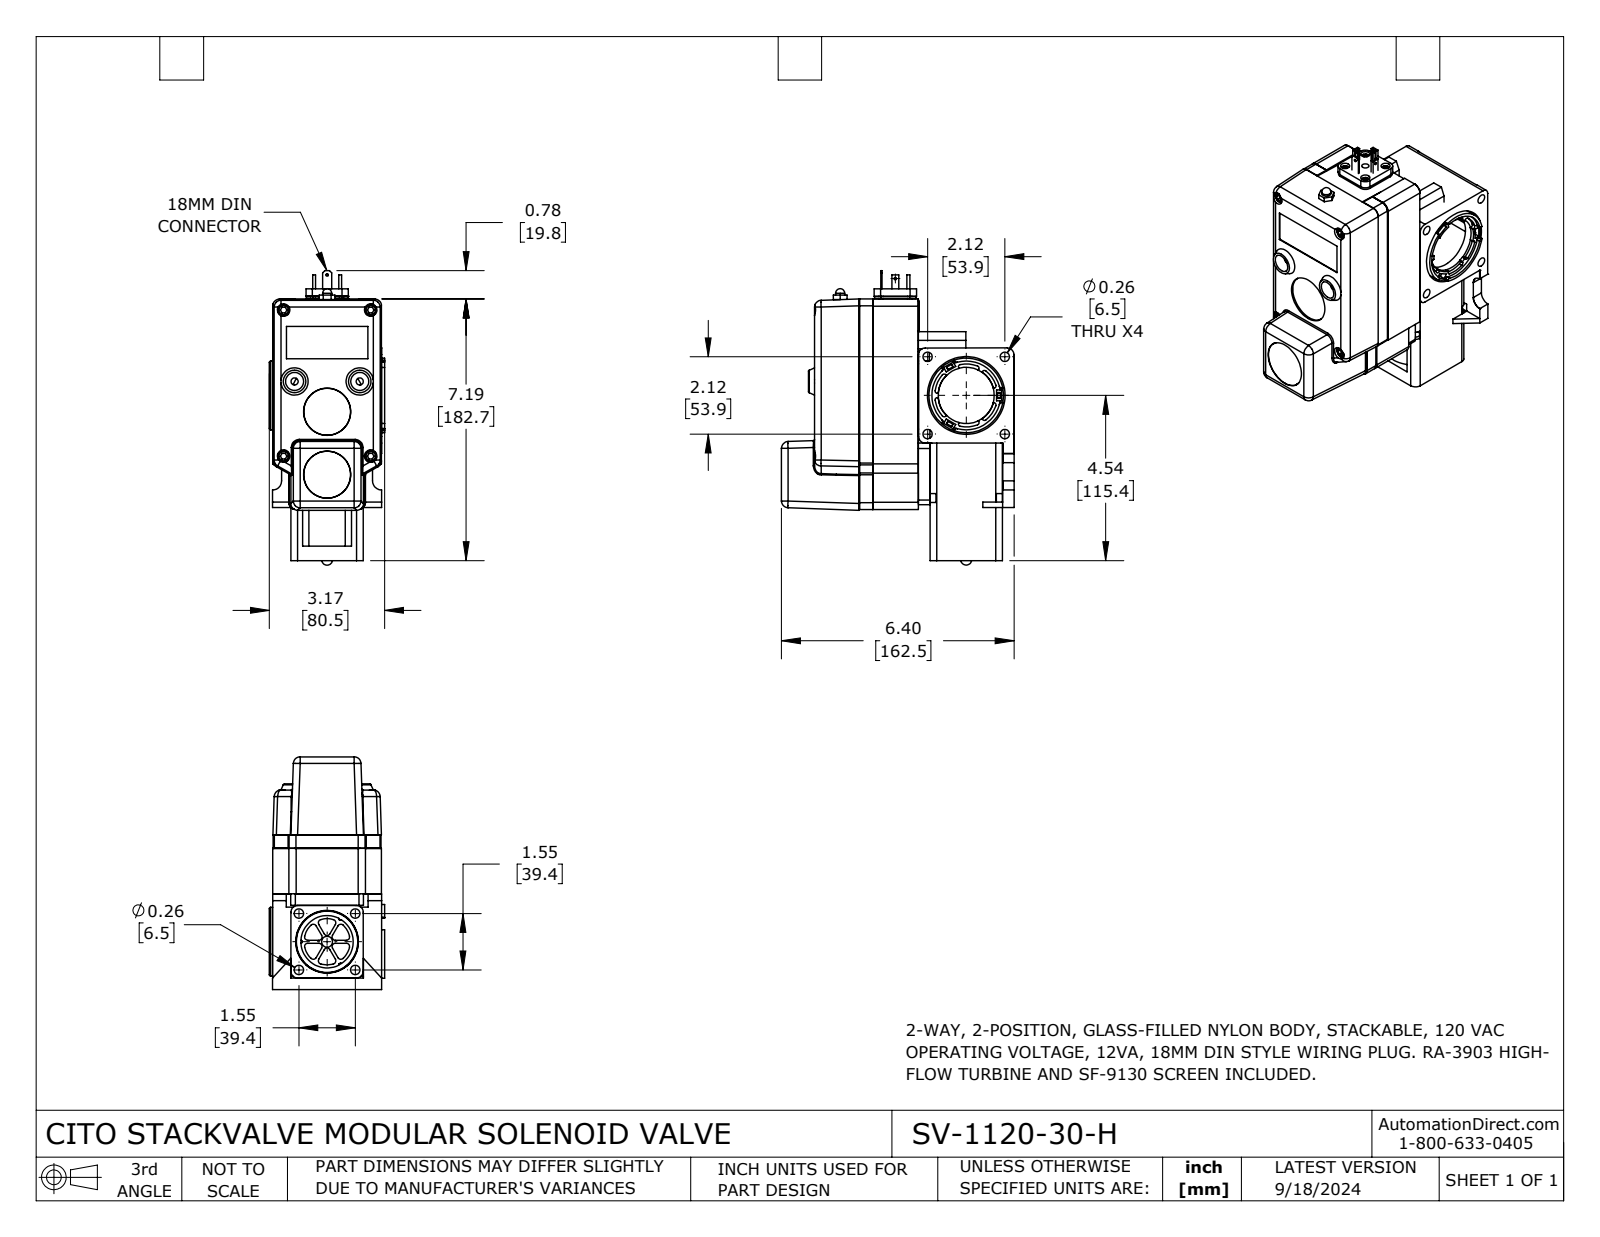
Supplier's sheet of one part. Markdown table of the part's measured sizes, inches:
| quantity | value |
| --- | --- |
| part name | SV-1120-30-H |
| STEP written by | SolidWorks 2023 (CONFIG_CONTROL_DESIGN) |
| units | inches |
| bodies | 27 solids, 1488 faces (728 planar, 504 cylindrical, 256 other) |
| overall size | 8.09 × 6.397 × 3.171 |
| volume | 43 in³ |
| surface area | 442.4 in² |
| round holes (diameter × count) | 0.218 × 13, 0.158 × 9, 0.138 × 6, 0.255 × 6, 0.25 × 4, 0.256 × 4, 0.257 × 4, 0.342 × 4, 0.066 × 3, 0.094 × 3, 0.196 × 2, 0.39 × 2 |
| round bosses / shafts (diameter × count) | 0.312 × 5, 0.19 × 5, 0.125 × 5, 0.245 × 4, 1.29 × 2, 2.6 × 1, 2.05 × 1, 1.65 × 1 |
| partial cylindrical surfaces (radius × count) | 0.062 × 19, 0.092 × 18, 0.188 × 13, 0.175 × 8, 0.1 × 7, 0.046 × 6, 0.187 × 6, 0.2 × 6 |
| main face-to-face distances | 2.49, 2.311, 0.15, 0.5, 3.882, 1.25, 1.45, 5.332, 1.99, 2.7 |
| hole center spacings | 1.591, 2.2, 2.4, 0.412, 0.557, 0.787, 1.135, 1.304 |
